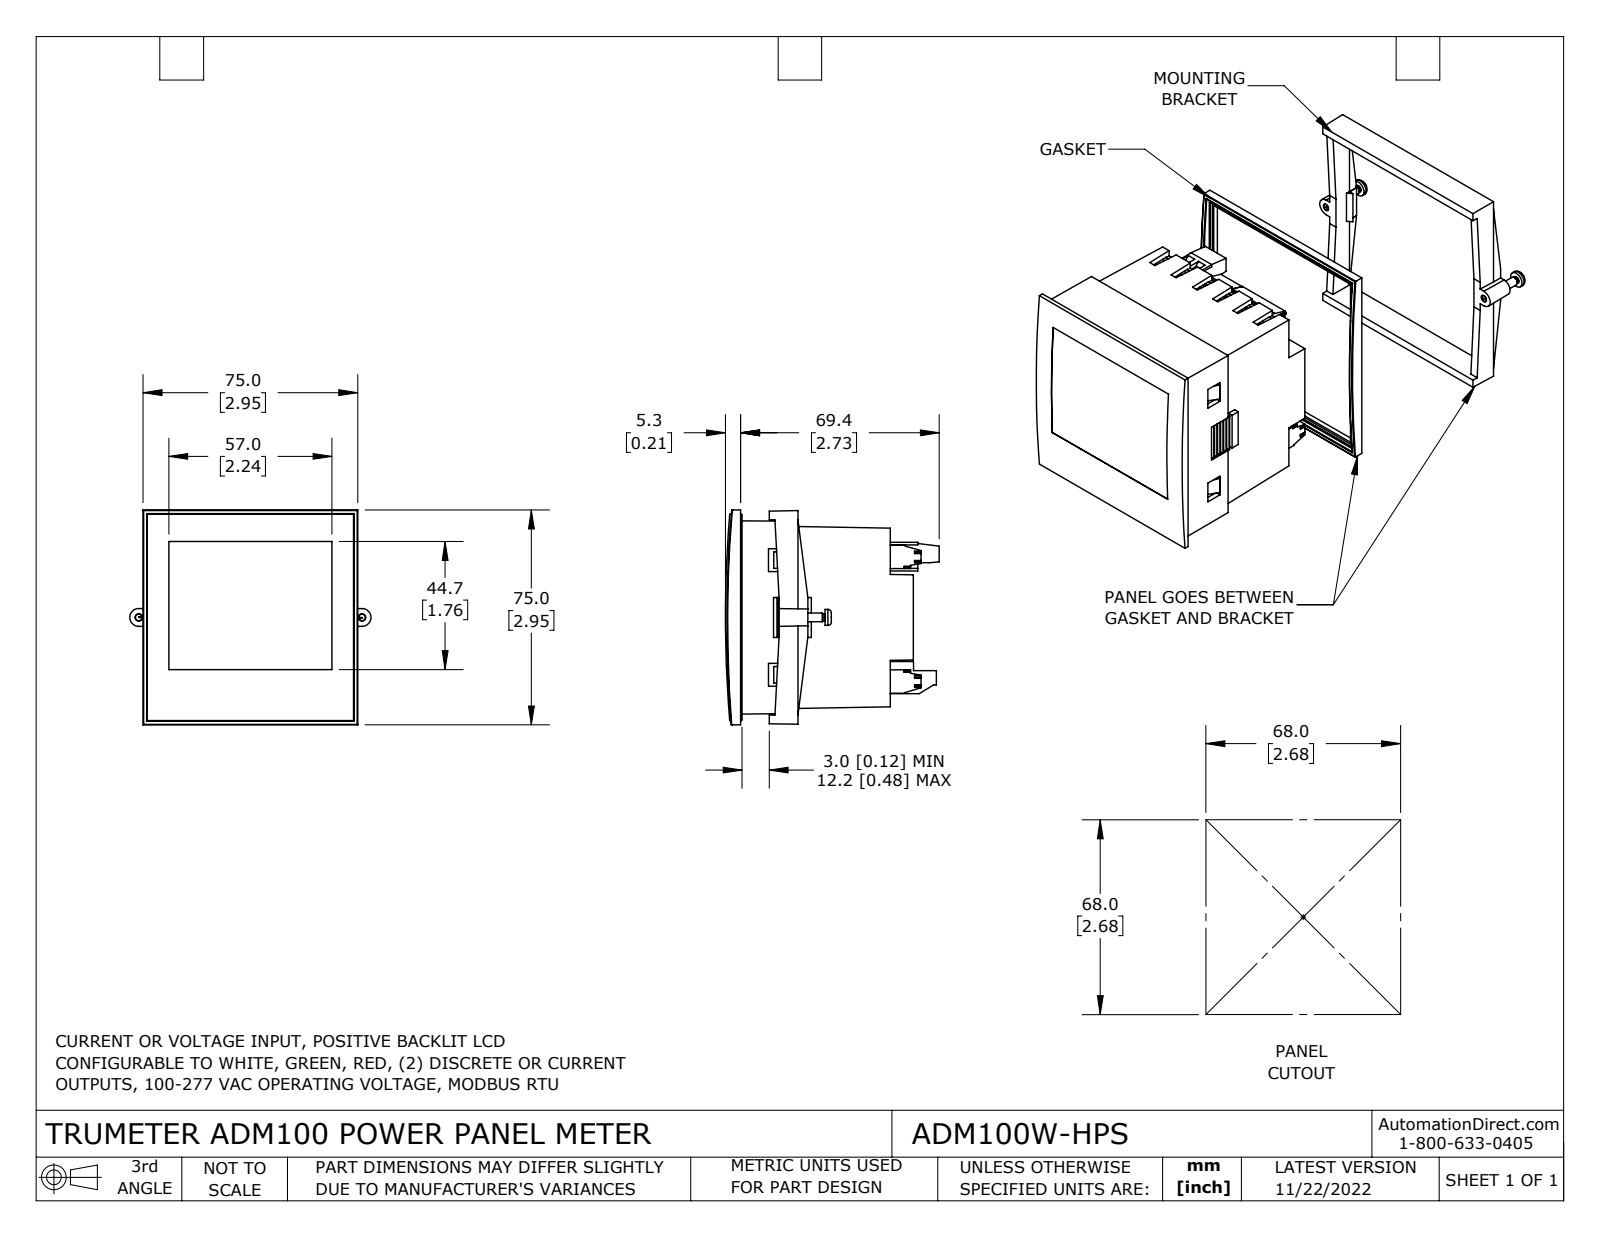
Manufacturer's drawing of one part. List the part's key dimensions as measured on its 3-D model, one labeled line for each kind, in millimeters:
Part name (STEP PRODUCT): ADM100W-HPS
STEP written by: SolidWorks 2021 (CONFIG_CONTROL_DESIGN)
Units: millimetres
Bodies: 12 solids, 1416 faces (1145 planar, 212 cylindrical, 59 other)
Overall size (bounding box): 84.2 × 75 × 74.7
Volume: 72 890 mm³ · Surface area: 75 230 mm²
Round holes (diameter × count): ⌀2.9 ×15, ⌀3 ×4, ⌀3.9 ×2
Round bosses / shafts (diameter × count): ⌀1 ×4, ⌀5.6 ×2, ⌀3 ×2, ⌀2.4 ×2
Partial cylindrical surfaces — rounded edges, fillets, slot ends (radius × count): R0.2 ×54, R0.2 ×4, R1.5 ×4, R432.7 ×1, R432.7 ×1, R456.2 ×1
Main face-to-face distances: 1.9, 62.1, 61.6, 63.5, 1.5, 65.5, 71.2, 5.5, 67.1, 69
Hole centre spacings: 3.5, 6.9, 10.3, 44.5, 43.9, 45.4, 13.8, 43.5
